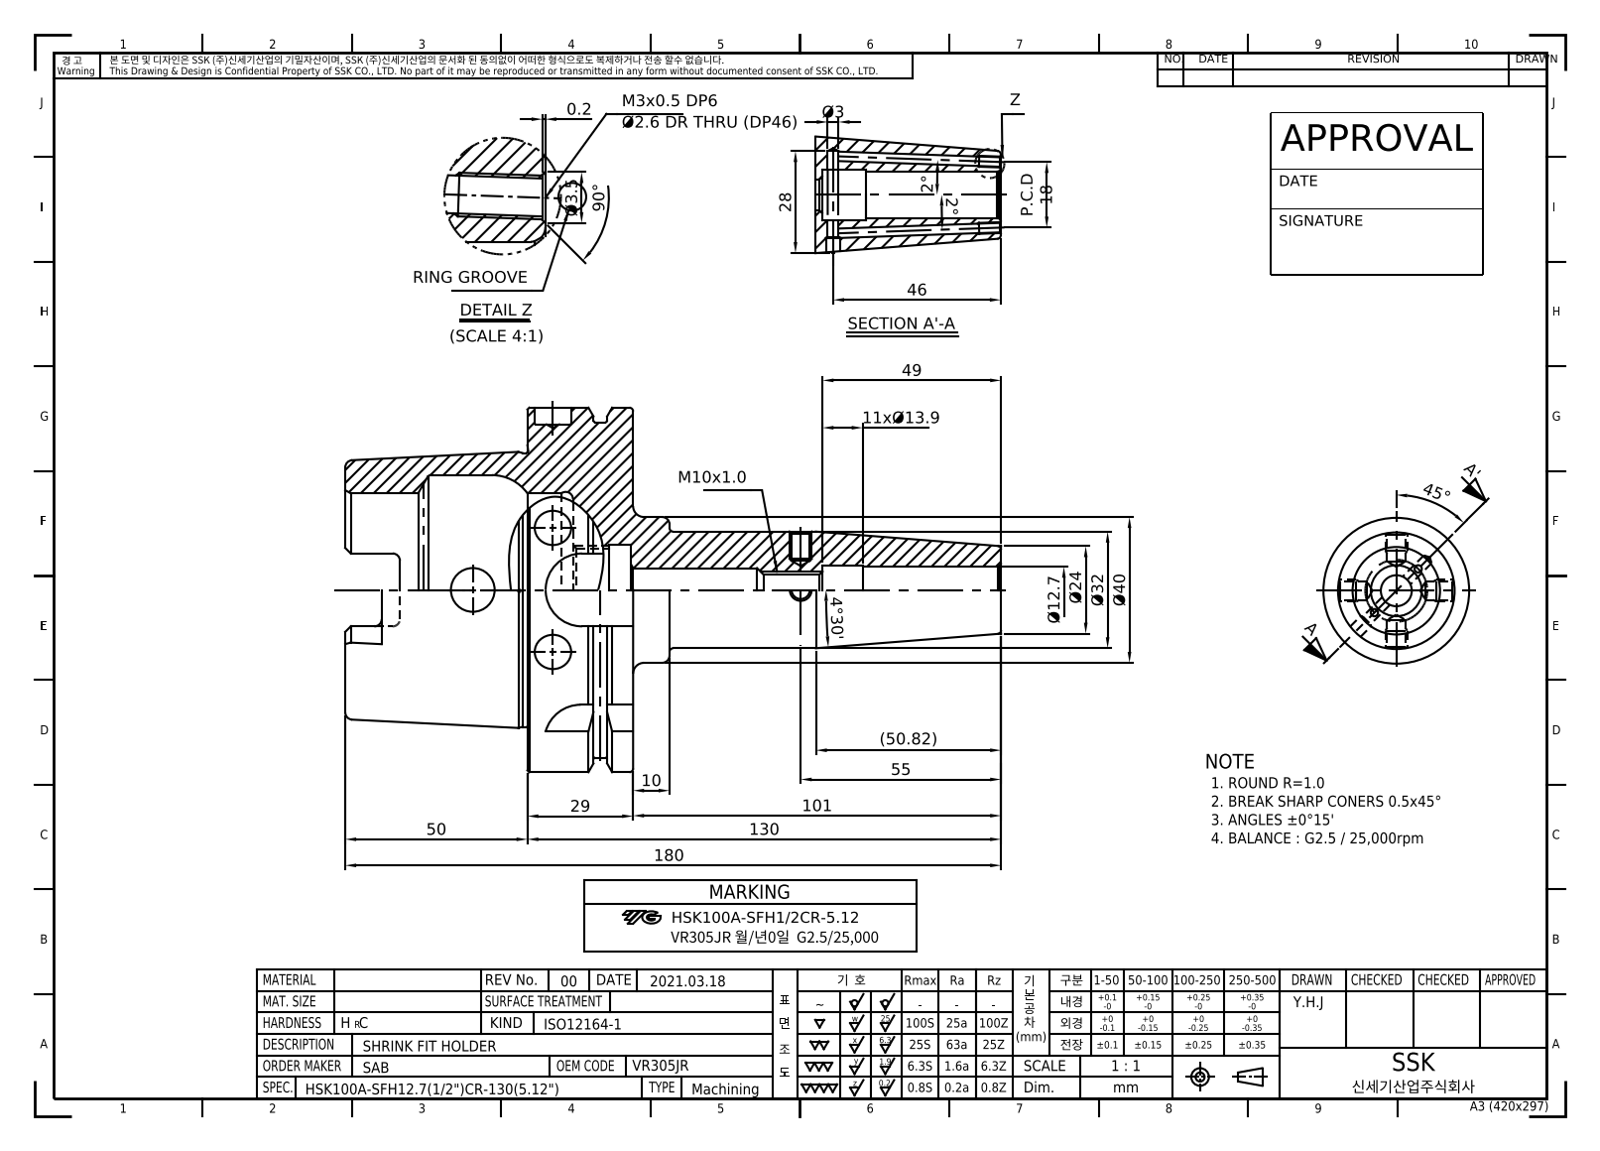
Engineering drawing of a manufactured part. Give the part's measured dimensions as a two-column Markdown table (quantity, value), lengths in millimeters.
| quantity | value |
| --- | --- |
| part name | LO-HSK100A-SFH12.7CR-130 |
| STEP written by | Autodesk Inventor 2022 (AUTOMOTIVE_DESIGN) |
| units | millimeters |
| bodies | 1 solid, 123 faces (39 planar, 38 cylindrical, 46 other) |
| overall size | 180 × 100 × 100 |
| volume | 318 749 mm³ |
| surface area | 63 200 mm² |
| round holes (diameter × count) | 2.46 × 2, 12 × 2, 8.92 × 1, 10 × 1, 12.7 × 1, 13.9 × 1, 22.38 × 1, 25 × 1, 53 × 1, 63 × 1 |
| round bosses / shafts (diameter × count) | 100 × 1, 92 × 1, 75.41 × 1, 40 × 1, 32 × 1 |
| partial cylindrical surfaces (radius × count) | 2 × 6, 4.88 × 4, 10 × 4 |
| main face-to-face distances | 29, 12.5, 16.5, 79, 62.5, 50, 88, 10, 78.5, 28.5 |
